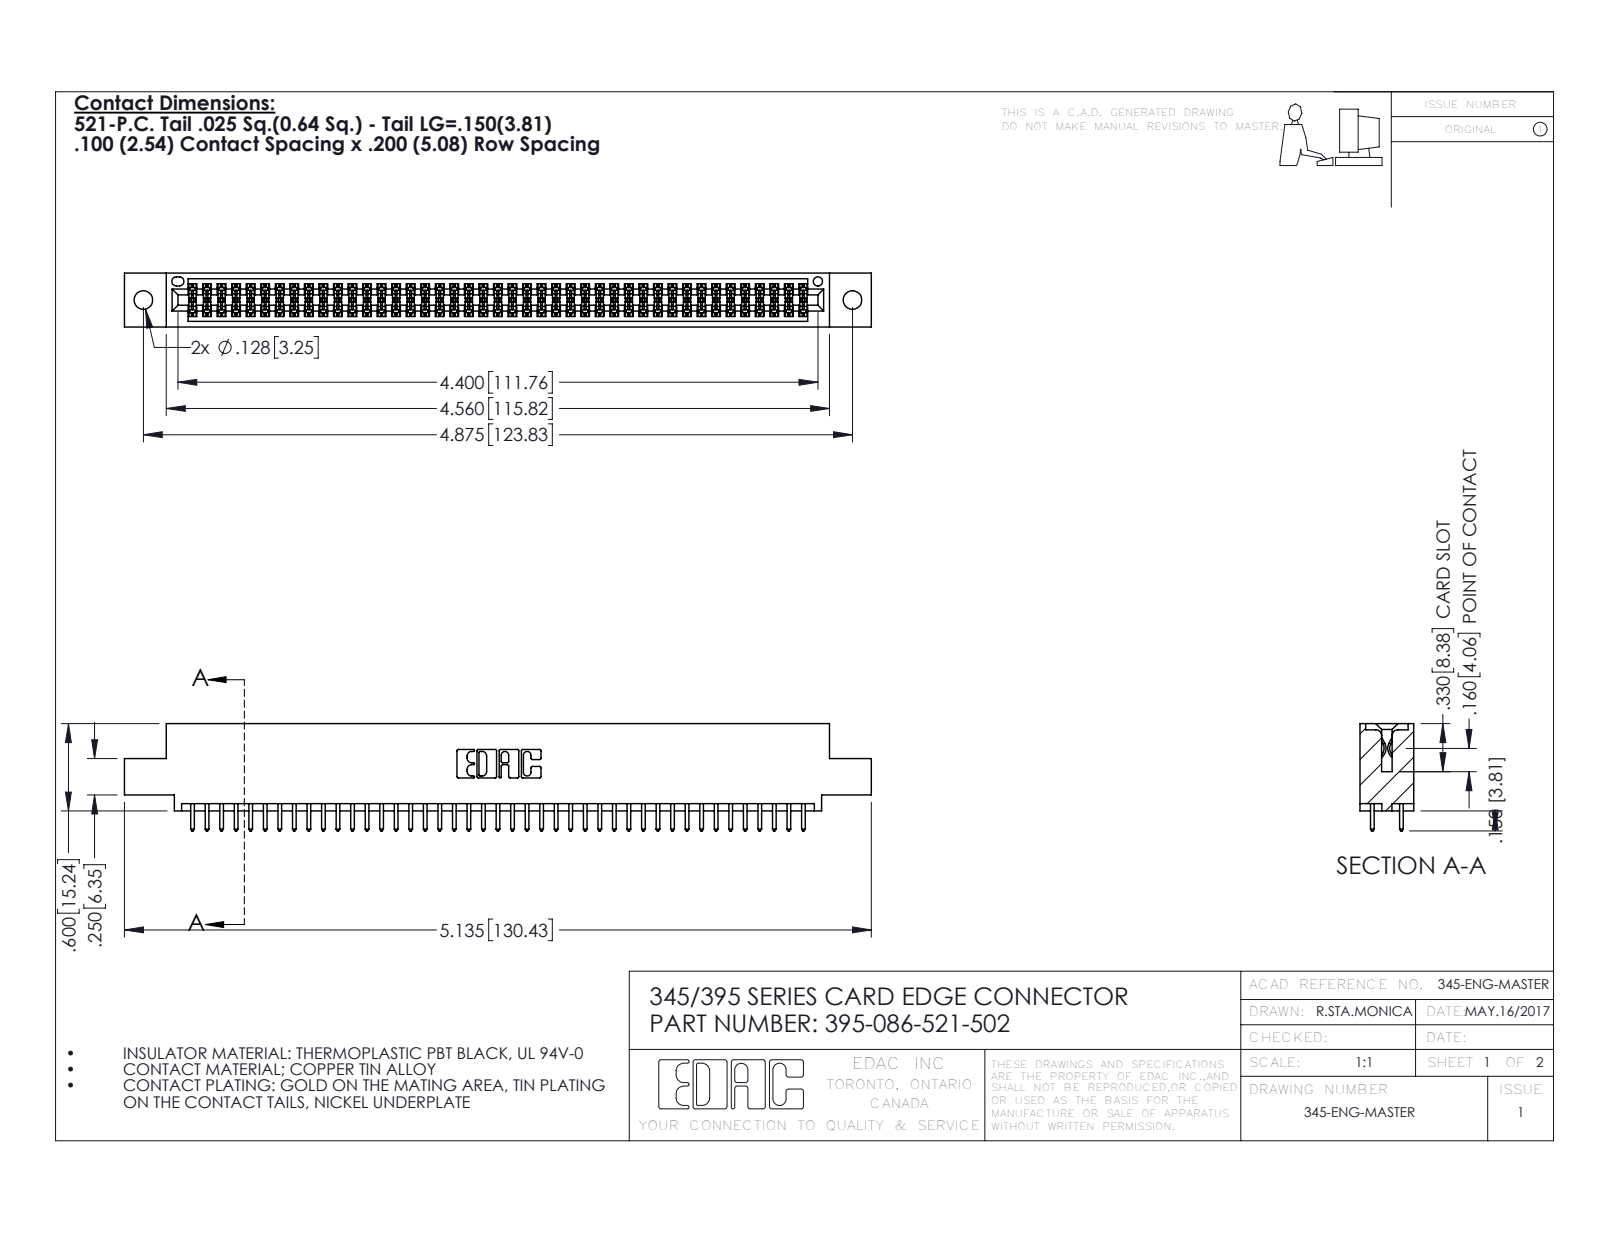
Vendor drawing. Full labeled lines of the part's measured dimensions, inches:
Part name (STEP PRODUCT): 345-292-001_345-293-121; 395-086-521-502; 345 Part_0.110 Offset - 0.128 Dia
STEP written by: SolidWorks 2016 (CONFIG_CONTROL_DESIGN)
Units: inches
Bodies: 87 solids, 4430 faces (2922 planar, 1508 cylindrical, 0 other)
Overall size (bounding box): 5.135 × 0.737 × 0.37
Volume: 0.765 in³ · Surface area: 28.11 in²
Round holes (diameter × count): ⌀0.128 ×2, ⌀0.064 ×1
Partial cylindrical surfaces — rounded edges, fillets, slot ends (radius × count): R0.006 ×129, R0.01 ×86, R0.01 ×22, R0.007 ×6, R0.031 ×6, R0.026 ×3, R0.014 ×2, R0.019 ×2
Main face-to-face distances: 0.298, 0.072, 0.2, 0.37, 0.098, 0.272, 0.025, 0.225, 0.175, 0.149
Hole centre spacings: 0.27, 4.639, 4.875
